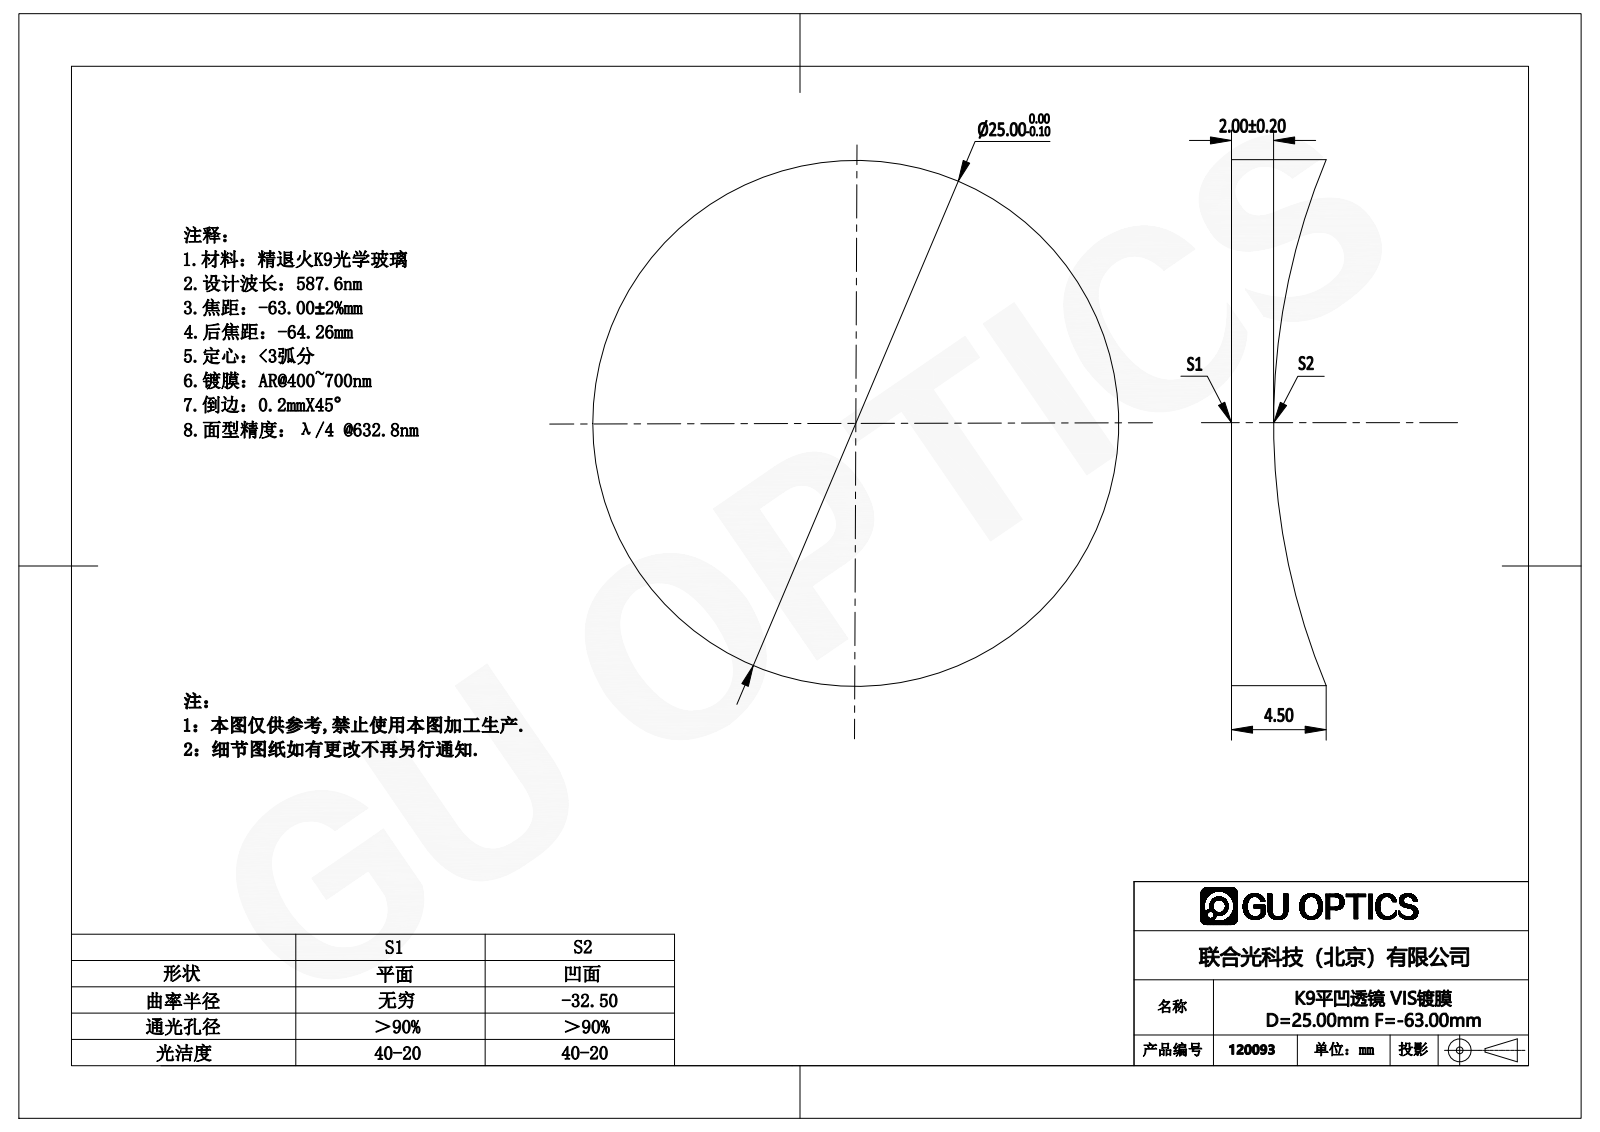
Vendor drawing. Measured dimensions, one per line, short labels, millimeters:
name: 120033
written by: SolidWorks 2016 (AUTOMOTIVE_DESIGN)
unit: mm
bodies: 1 solid, 5 faces (1 planar, 2 cylindrical, 2 other)
size: 25 × 25 × 4.5
volume: 1 587 mm³; area: 1 355 mm²
bosses: 1× ⌀25
